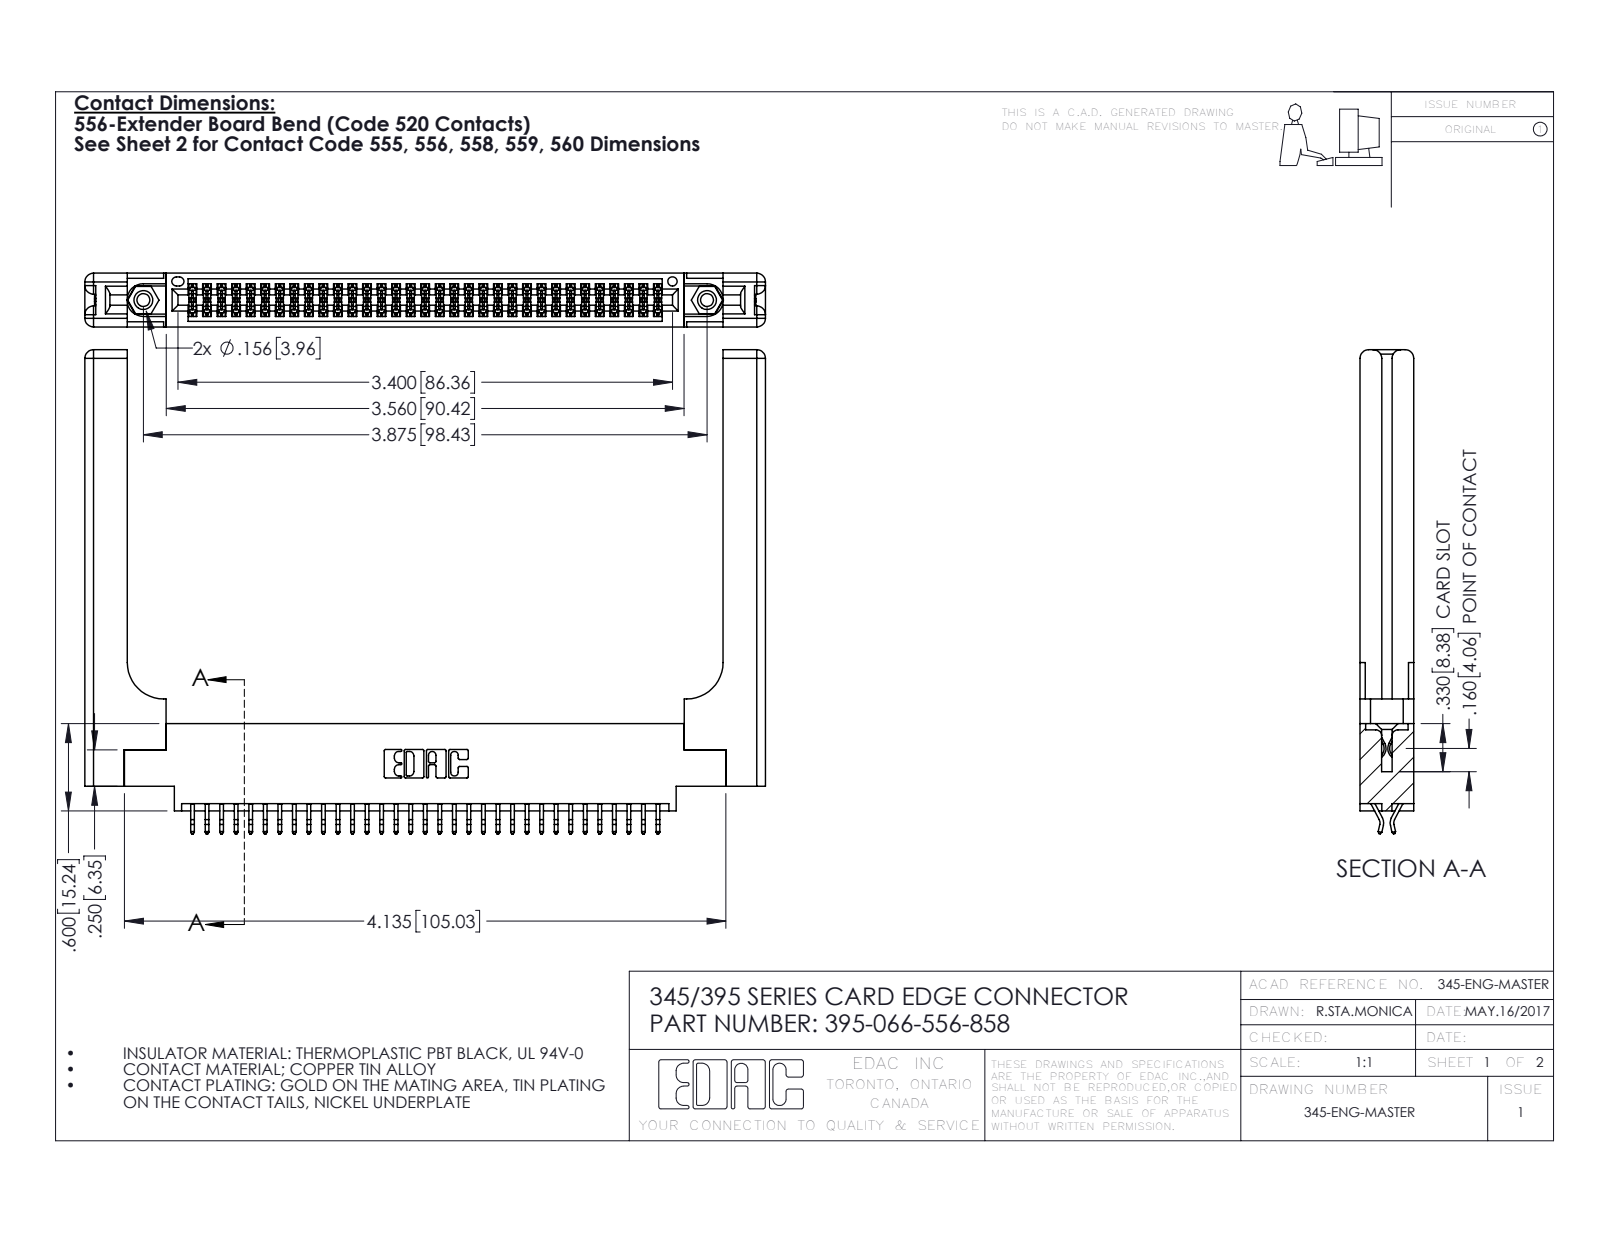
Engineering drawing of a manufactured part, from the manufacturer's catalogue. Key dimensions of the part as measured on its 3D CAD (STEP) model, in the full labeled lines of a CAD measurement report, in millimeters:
Part name (STEP PRODUCT): 345 Part_0.170 Offset - 0.156 Dia-TH; 345-292-001_556 Tail; 395-066-556-858; 345-250-001_345-250-001-102 (+1 more)
STEP written by: SolidWorks 2016 (CONFIG_CONTROL_DESIGN)
Units: millimetres
Bodies: 71 solids, 4082 faces (2674 planar, 1348 cylindrical, 60 other)
Overall size (bounding box): 118.8 × 84.5 × 9.4
Volume: 19 830 mm³ · Surface area: 21 740 mm²
Round holes (diameter × count): ⌀2.3 ×2, ⌀3.2 ×2, ⌀4 ×2, ⌀1.6 ×1
Round bosses / shafts (diameter × count): ⌀3.9 ×2
Partial cylindrical surfaces — rounded edges, fillets, slot ends (radius × count): R0.2 ×99, R0.3 ×22, R1.5 ×16, R0.2 ×6, R0.8 ×6, R0.7 ×3, R0.3 ×2, R0.4 ×2
Main face-to-face distances: 9.4, 1.8, 7.6, 0.6, 5.7, 2.5, 6.9, 5.1, 3.8, 3.8
Hole centre spacings: 6.9, 92.5, 98.4
